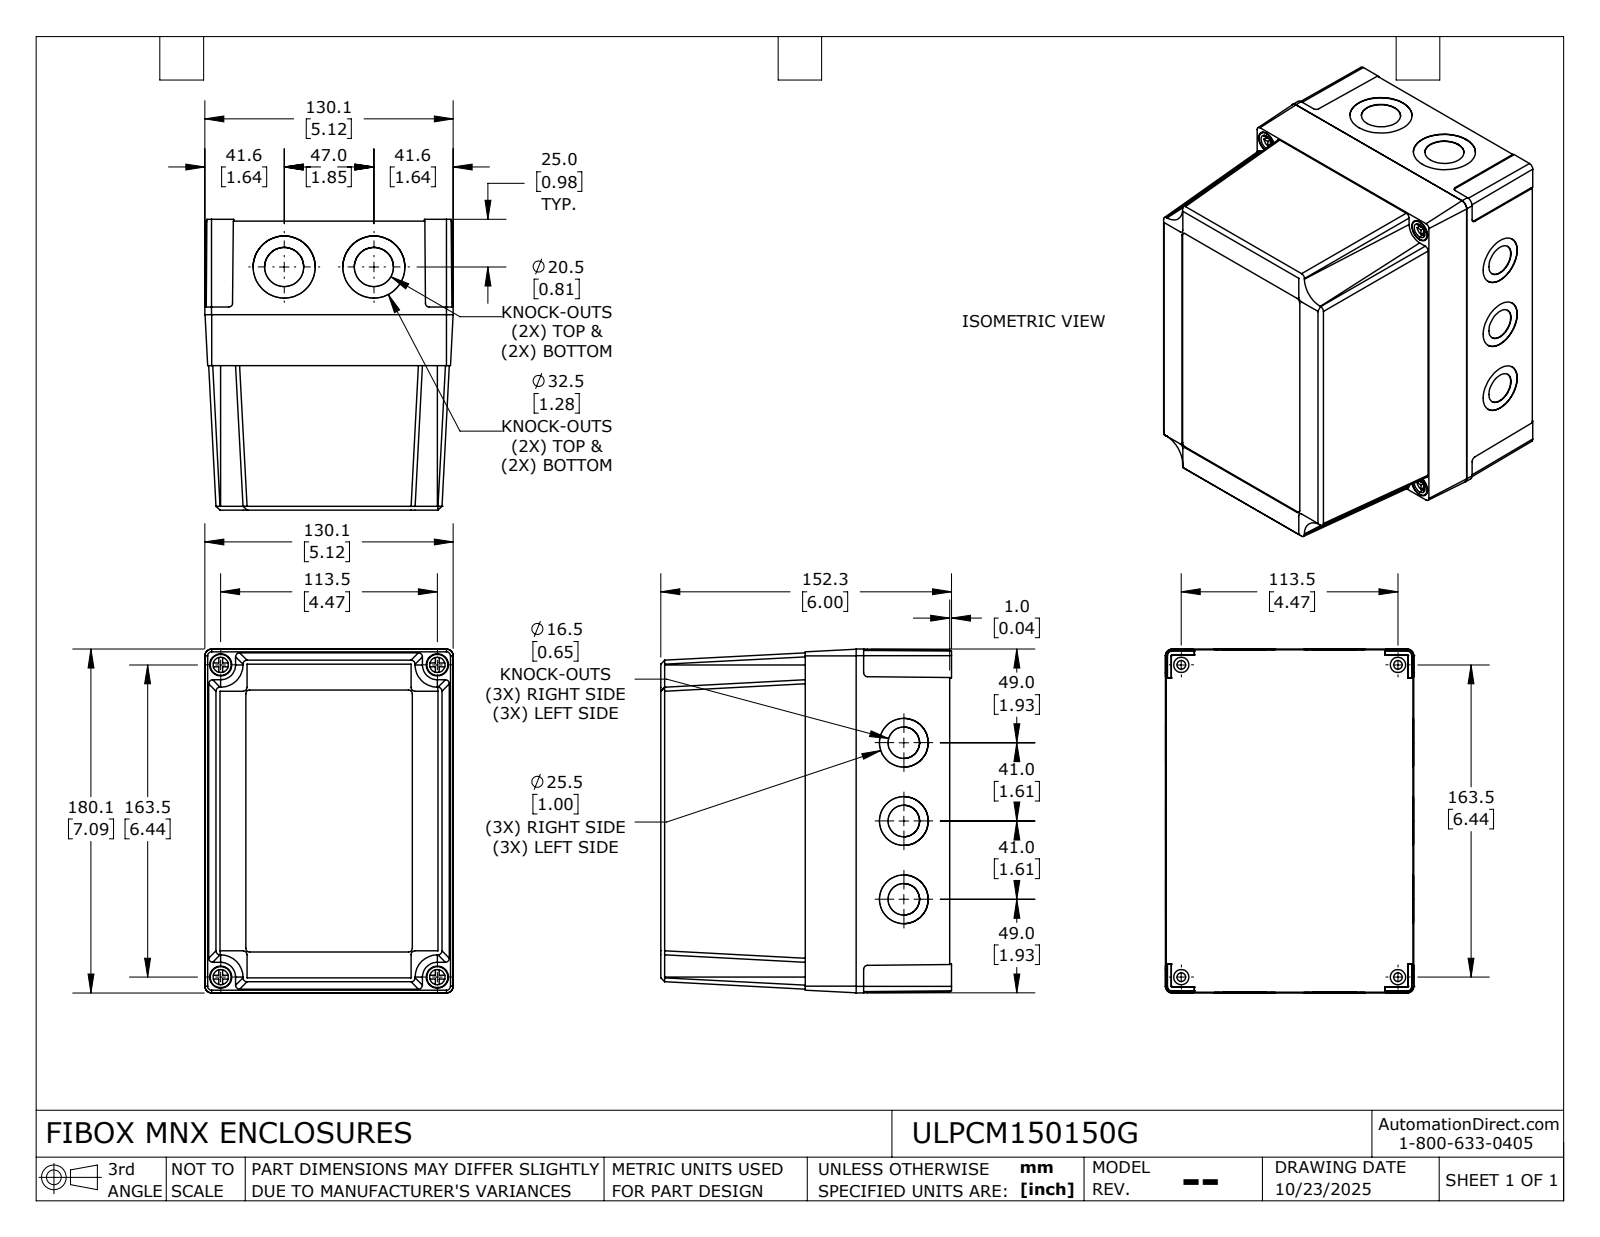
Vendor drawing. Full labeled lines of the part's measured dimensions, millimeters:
Part name (STEP PRODUCT): ULPCM150150G_Default
STEP written by: SolidWorks 2024 (CONFIG_CONTROL_DESIGN)
Units: millimetres
Bodies: 6 solids, 585 faces (339 planar, 200 cylindrical, 46 other)
Overall size (bounding box): 180.1 × 152.3 × 130.1
Volume: 403 100 mm³ · Surface area: 275 200 mm²
Round holes (diameter × count): ⌀3.2 ×8, ⌀4 ×8, ⌀16.5 ×6, ⌀25.5 ×6, ⌀4.5 ×4, ⌀8 ×4, ⌀11.6 ×4, ⌀20.5 ×4, ⌀32.5 ×4
Round bosses / shafts (diameter × count): ⌀8 ×8, ⌀2.5 ×8, ⌀11 ×4, ⌀7.2 ×4
Partial cylindrical surfaces — rounded edges, fillets, slot ends (radius × count): R2 ×8, R2.1 ×8, R1.4 ×6, R0.5 ×4, R5 ×4, R0.6 ×2
Main face-to-face distances: 2, 3, 148.3, 4.2, 145.3, 2.5, 150.8, 147.8, 2.6, 0.6
Hole centre spacings: 33.9, 41, 49.3, 50, 57.9, 82.6, 83.2, 103
